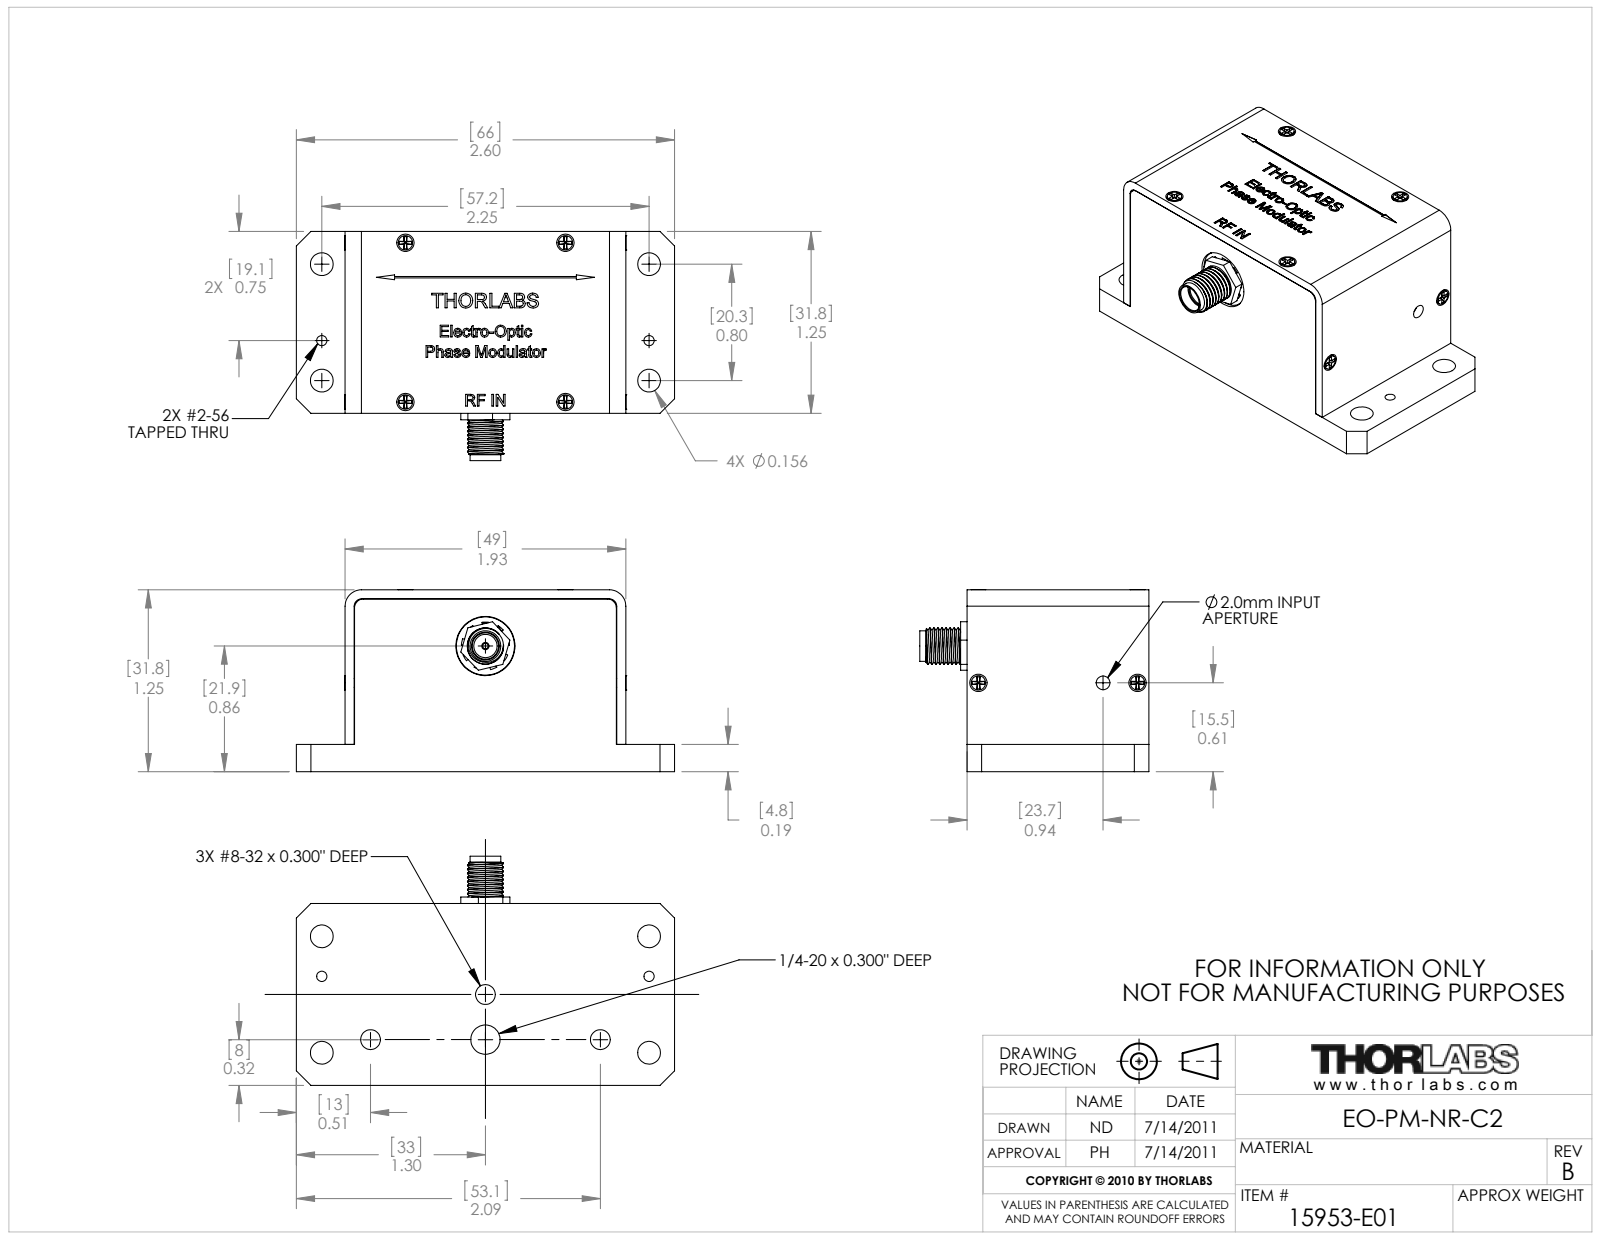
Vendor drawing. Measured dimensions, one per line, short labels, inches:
name: 15953-E01
written by: SolidWorks 2011 (AUTOMOTIVE_DESIGN)
unit: in
bodies: 13 solids, 997 faces (529 planar, 171 cylindrical, 297 other)
size: 2.6 × 1.575 × 1.252
volume: 1.741 in³; area: 28.94 in²
holes: 8× ⌀0.07, 6× ⌀0.047, 4× ⌀0.156, 3× ⌀0.136, 1× ⌀0.037, 1× ⌀0.05, 1× ⌀0.094, 1× ⌀0.16, 1× ⌀0.165, 1× ⌀0.181, 1× ⌀0.201, 1× ⌀0.25
bosses: 6× ⌀0.099, 6× ⌀0.06, 1× ⌀0.4, 1× ⌀0.315, 1× ⌀0.248, 1× ⌀0.21, 1× ⌀0.05
rounds: 2× R0.05, 2× R0.063, 2× R0.113, 2× R0.125, 2× R0.128, 1× R0.137, 1× R0.165
face distances: 1.25, 0.125, 1.125, 1.188, 0.063, 1.867, 1, 0.062, 0.35, 0.838
hole spacings: 0.594, 0.776, 1.108, 1.194, 1.681, 1.924, 1.094, 2.25
